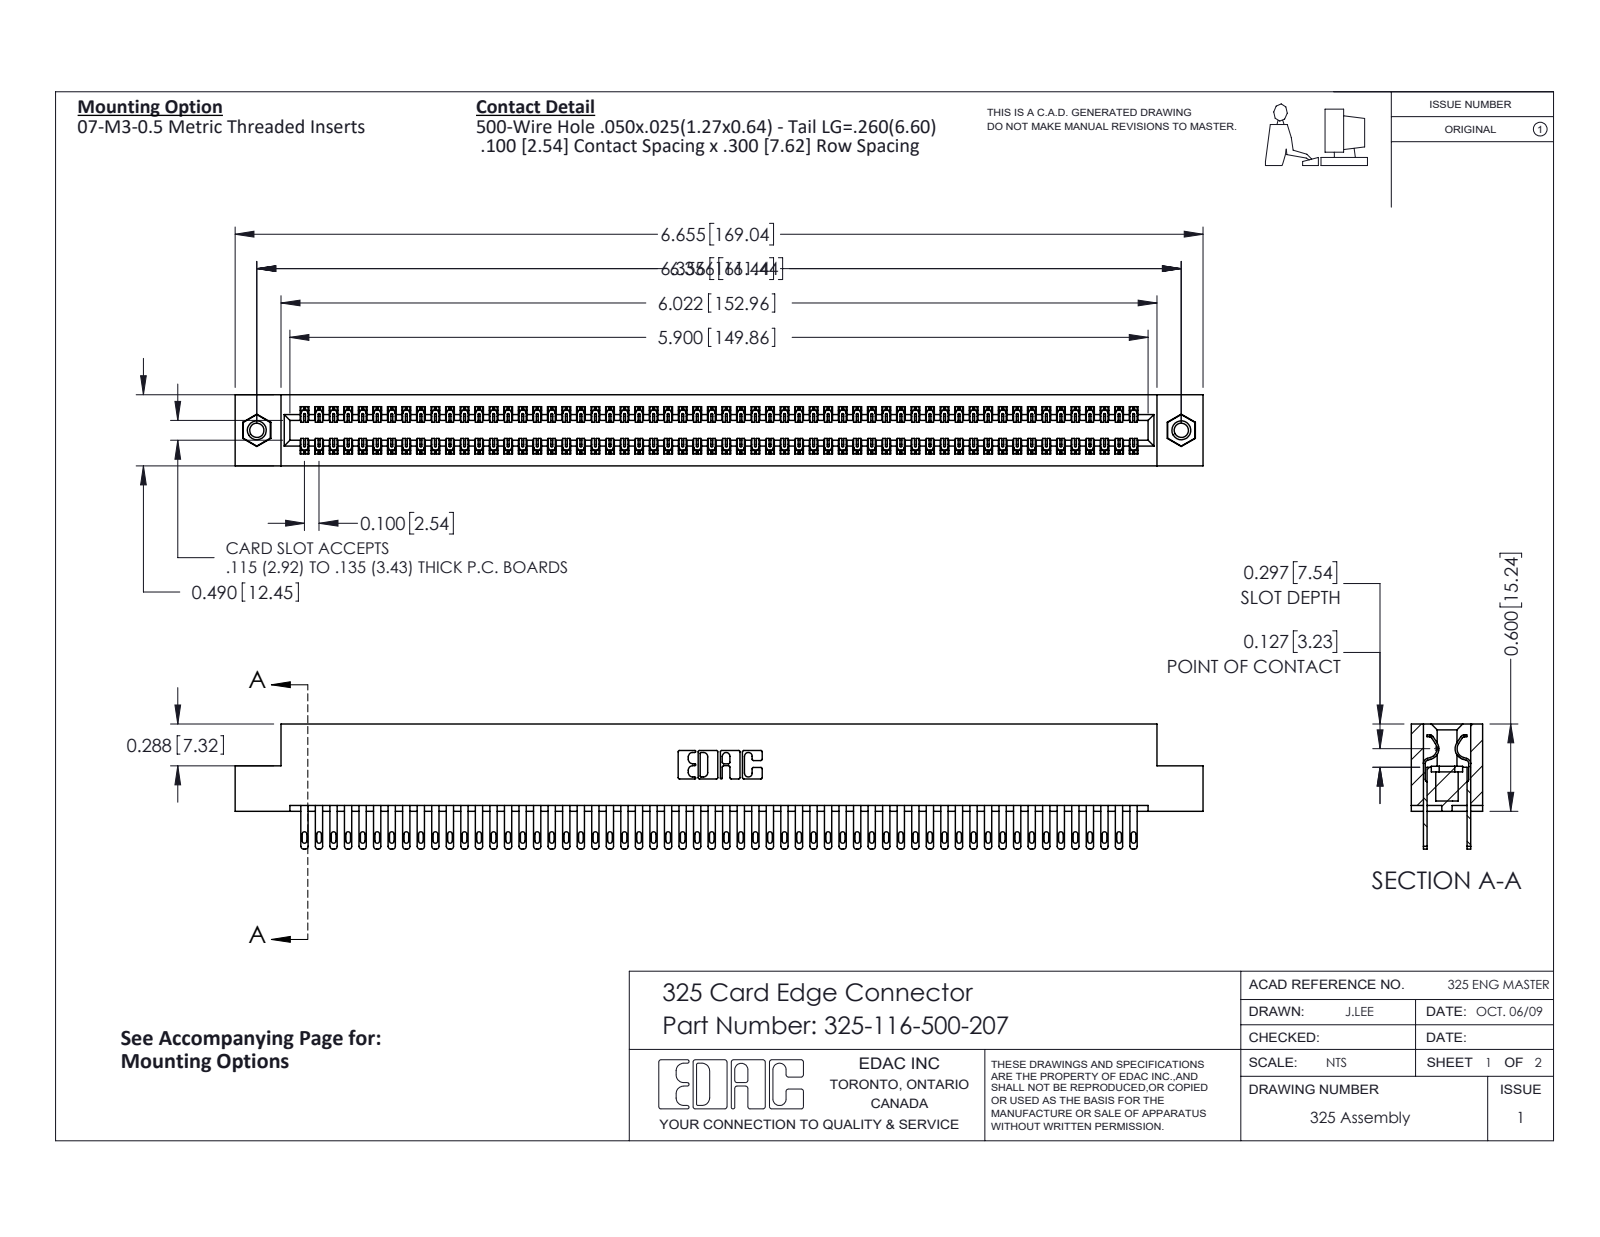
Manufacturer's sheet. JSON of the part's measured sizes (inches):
{"part_name": "345-250-001_345-250-005-103; 325 Part_TI; 325-292-001_325-293-100; 325-116-500-207", "step_written_by": "SolidWorks 2016 (CONFIG_CONTROL_DESIGN)", "units": "inches", "bodies": {"solids": 119, "faces": 5742, "planar": 3582, "cylindrical": 2144, "other": 16}, "overall_size": [6.655, 0.86, 0.49], "volume_in3": 1.361, "surface_area_in2": 44.36, "round_holes": [[0.098, 2], [0.125, 2], [0.16, 2]], "round_bosses_or_shafts": [[0.155, 2]], "partial_cylinders_radius": [[0.006, 174], [0.016, 116], [0.02, 116], [0.01, 22], [0.007, 6], [0.031, 6], [0.026, 3], [0.014, 2]], "face_to_face_distances": [0.083, 0.407, 0.3, 0.107, 0.383, 0.025, 0.49, 0.325, 0.275, 0.263], "hole_center_spacings": [6.356]}
